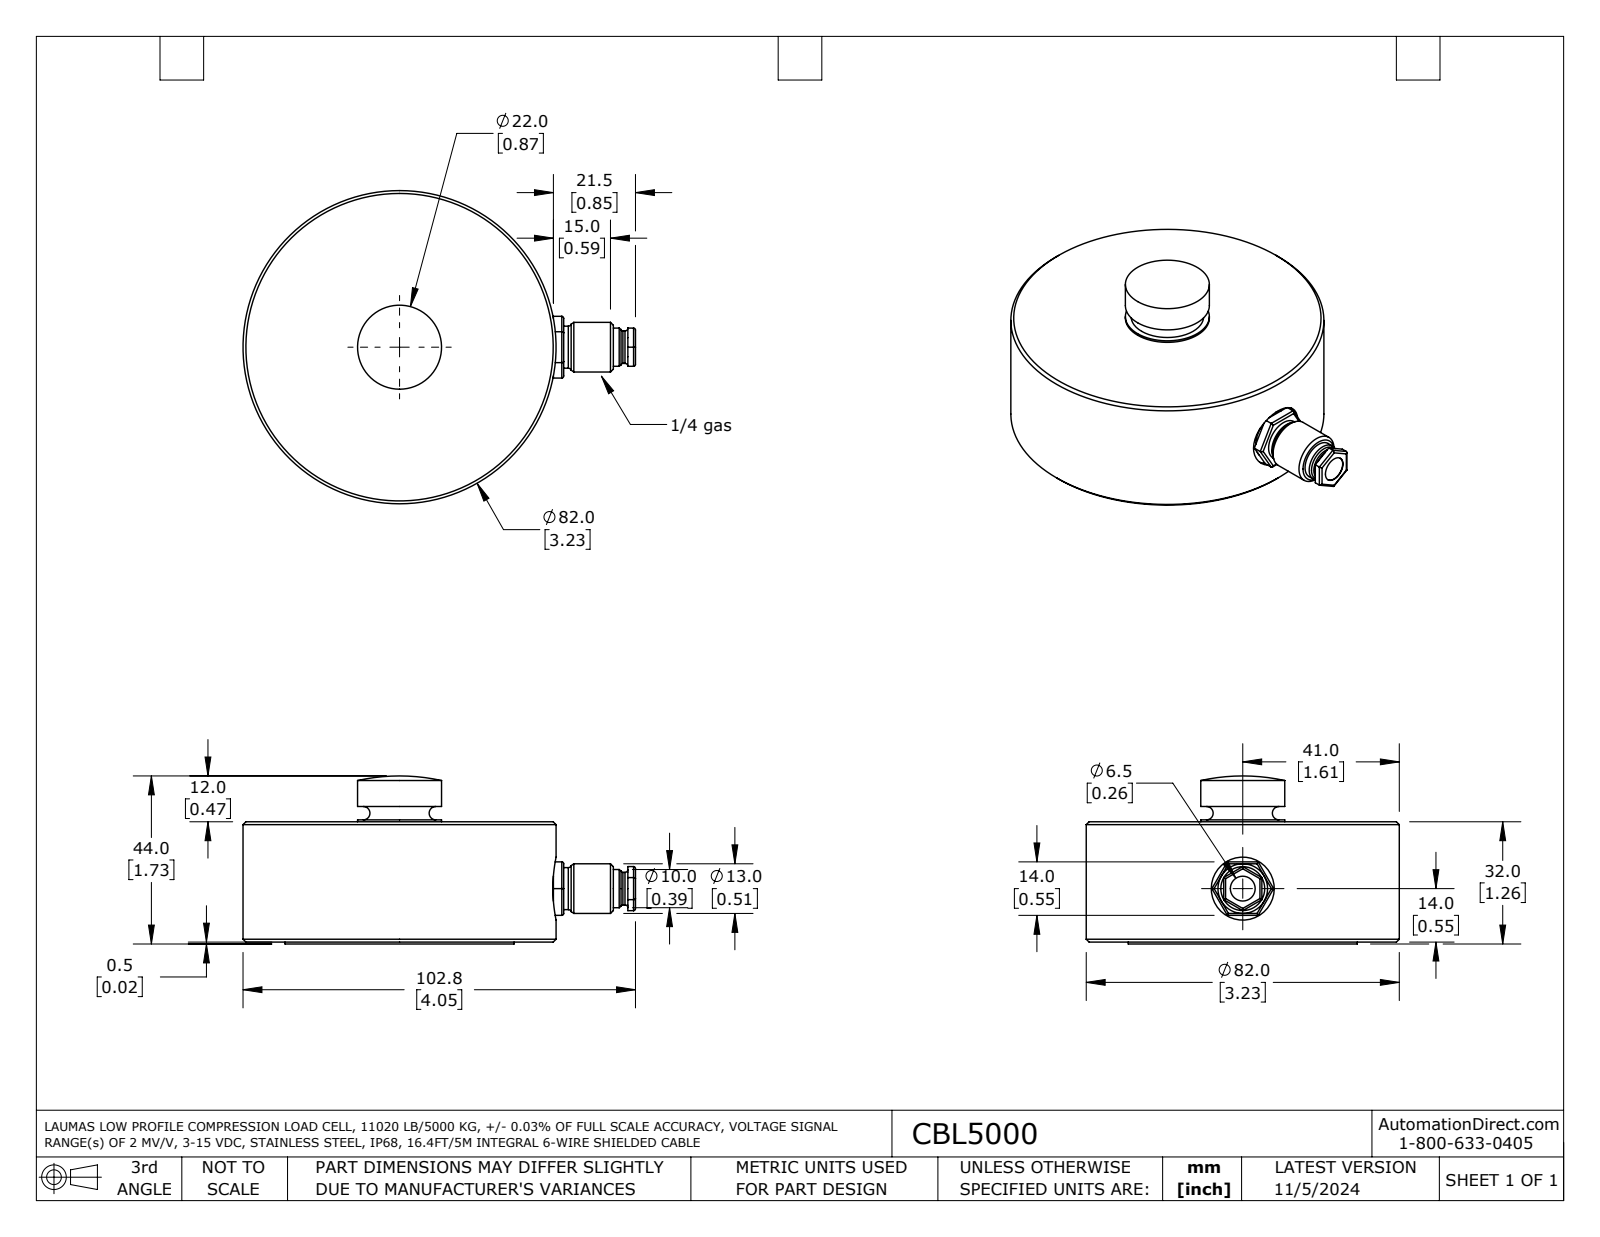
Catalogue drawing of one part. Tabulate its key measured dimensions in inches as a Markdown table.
| quantity | value |
| --- | --- |
| part name | CBL5000 |
| STEP written by | SolidWorks 2021 (AUTOMOTIVE_DESIGN) |
| units | inches |
| bodies | 2 solids, 86 faces (31 planar, 36 cylindrical, 19 other) |
| overall size | 4.047 × 3.228 × 1.732 |
| volume | 10.42 in³ |
| surface area | 32.65 in² |
| round holes (diameter × count) | 0.256 × 1, 0.65 × 1, 2.15 × 1 |
| round bosses / shafts (diameter × count) | 3.228 × 1, 2.362 × 1, 0.866 × 1, 0.531 × 1, 0.512 × 1, 0.433 × 1, 0.394 × 1, 0.335 × 1 |
| partial cylindrical surfaces (radius × count) | 0.02 × 12 |
| main face-to-face distances | 1.211, 0.03, 1.24, 0.02, 1.26, 0.049, 0.138, 1.28, 1.23, 1.417 |
